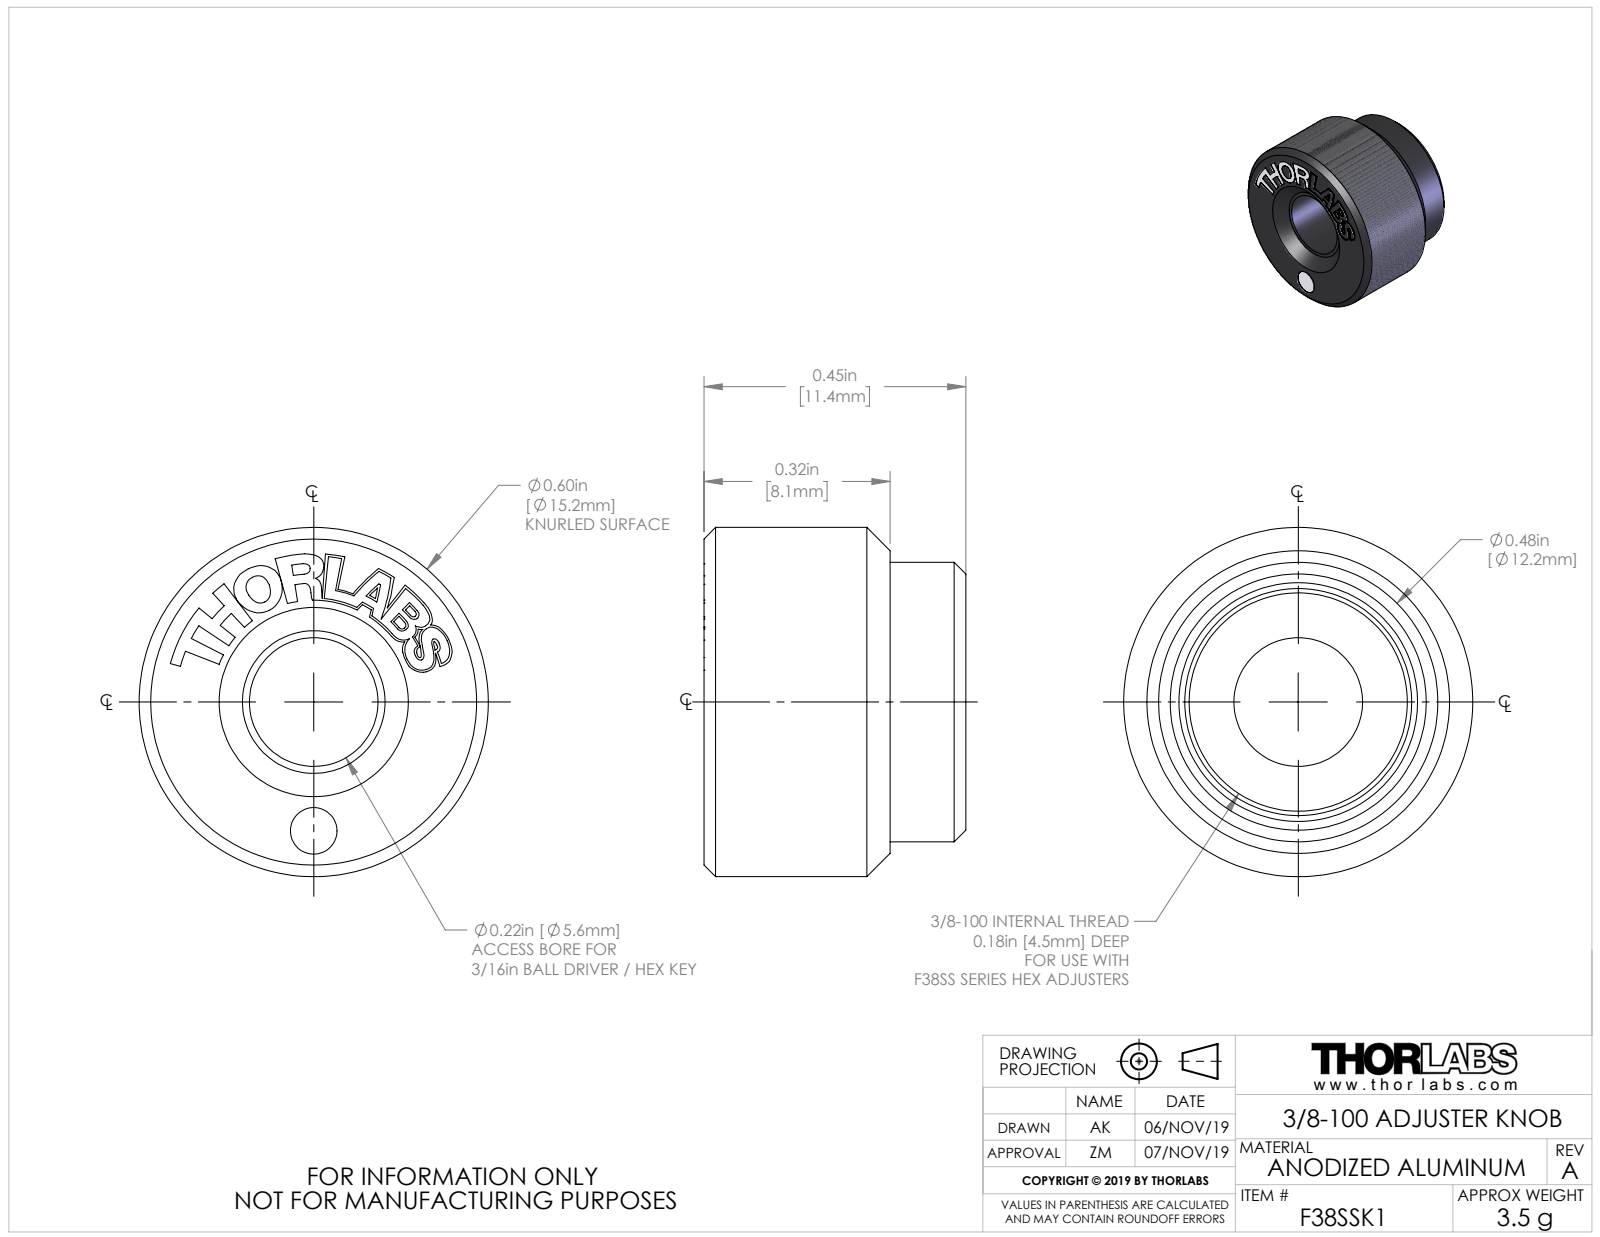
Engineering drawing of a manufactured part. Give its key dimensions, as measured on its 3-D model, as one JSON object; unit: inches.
{"part_name": "TTN200030-E0W", "step_written_by": "SolidWorks 2018 (AUTOMOTIVE_DESIGN)", "units": "inches", "bodies": {"solids": 1, "faces": 189, "planar": 51, "cylindrical": 14, "other": 124}, "overall_size": [0.6, 0.6, 0.45], "volume_in3": 0.08, "surface_area_in2": 1.622, "round_holes": [[0.08, 1], [0.221, 1], [0.375, 1], [0.39, 1], [0.405, 1]], "round_bosses_or_shafts": [[0.6, 1], [0.48, 1]], "face_to_face_distances": [0.27, 0.32, 0.05, 0.269, 0.319, 0.45, 0.449, 0.18, 0.13, 0.285], "hole_center_spacings": [0.221]}
